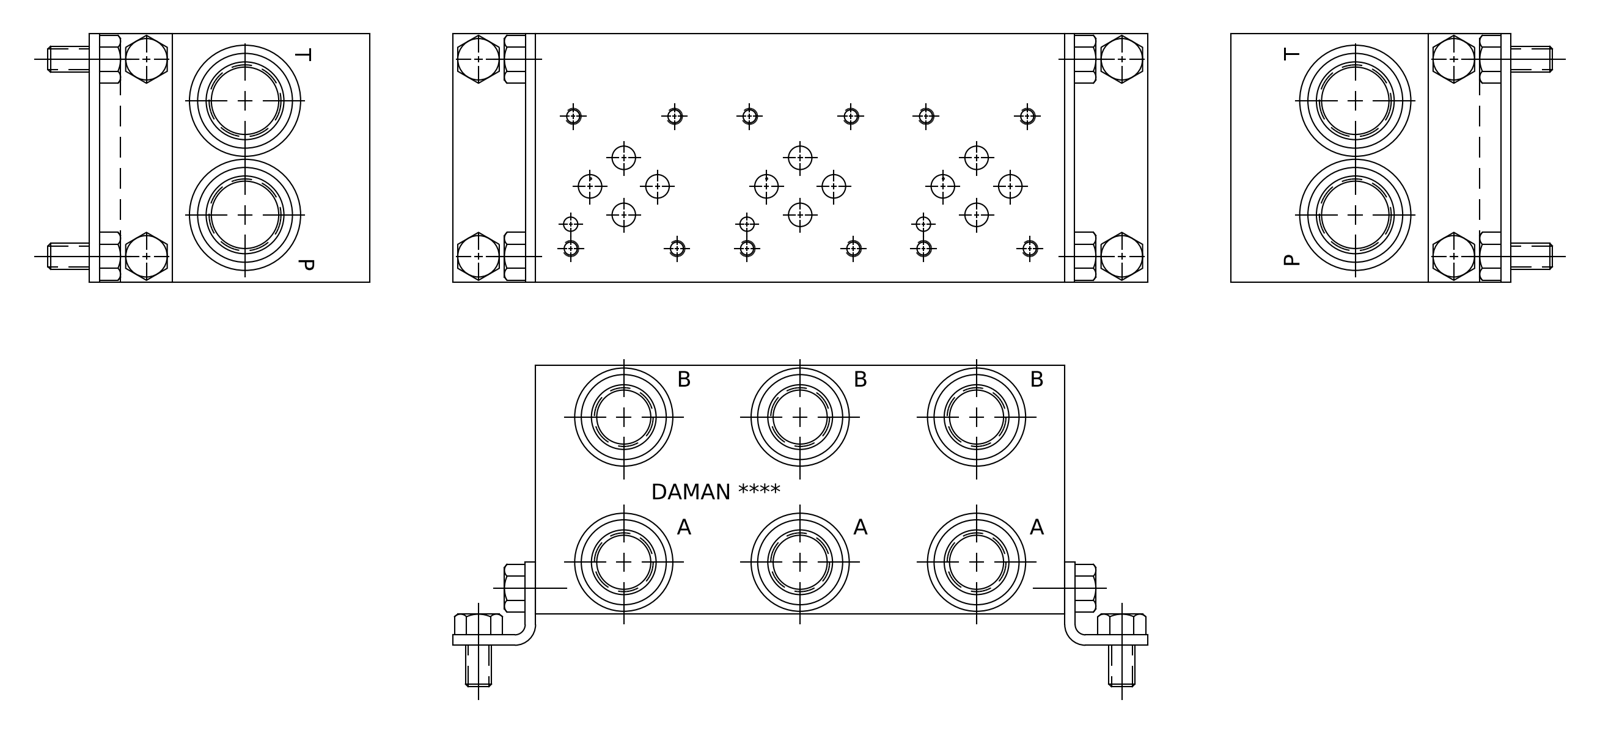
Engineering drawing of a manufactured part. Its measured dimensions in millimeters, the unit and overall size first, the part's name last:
Units: millimetres
Overall size (bounding box): 161.67 × 76.2 × 76.2
Round holes (diameter × count): ⌀4.22 ×12, ⌀5 ×12, ⌀7.14 ×9, ⌀14.27 ×6, ⌀16.54 ×6, ⌀18.01 ×6, ⌀30 ×6, ⌀3.96 ×3, ⌀6.35 ×3, ⌀6.76 ×2, ⌀8 ×2, ⌀19.05 ×2
Main face-to-face distances: 76.2, 0.79, 161.67, 75.41, 160.88, 160.09, 15.29, 14.5, 60.91, 0.75
Hole centre spacings: 53.72, 19.95, 22.05, 33.55, 40.49, 51.45, 53.98, 107.7
Volume: 855 525 mm³ · Surface area: 80 891 mm²
Bodies: 1 solid, 690 faces (373 planar, 91 cylindrical, 226 other)
Part name (STEP PRODUCT): Part_AD03P032M_3D
STEP written by: Autodesk Inventor 2021 (AUTOMOTIVE_DESIGN)
